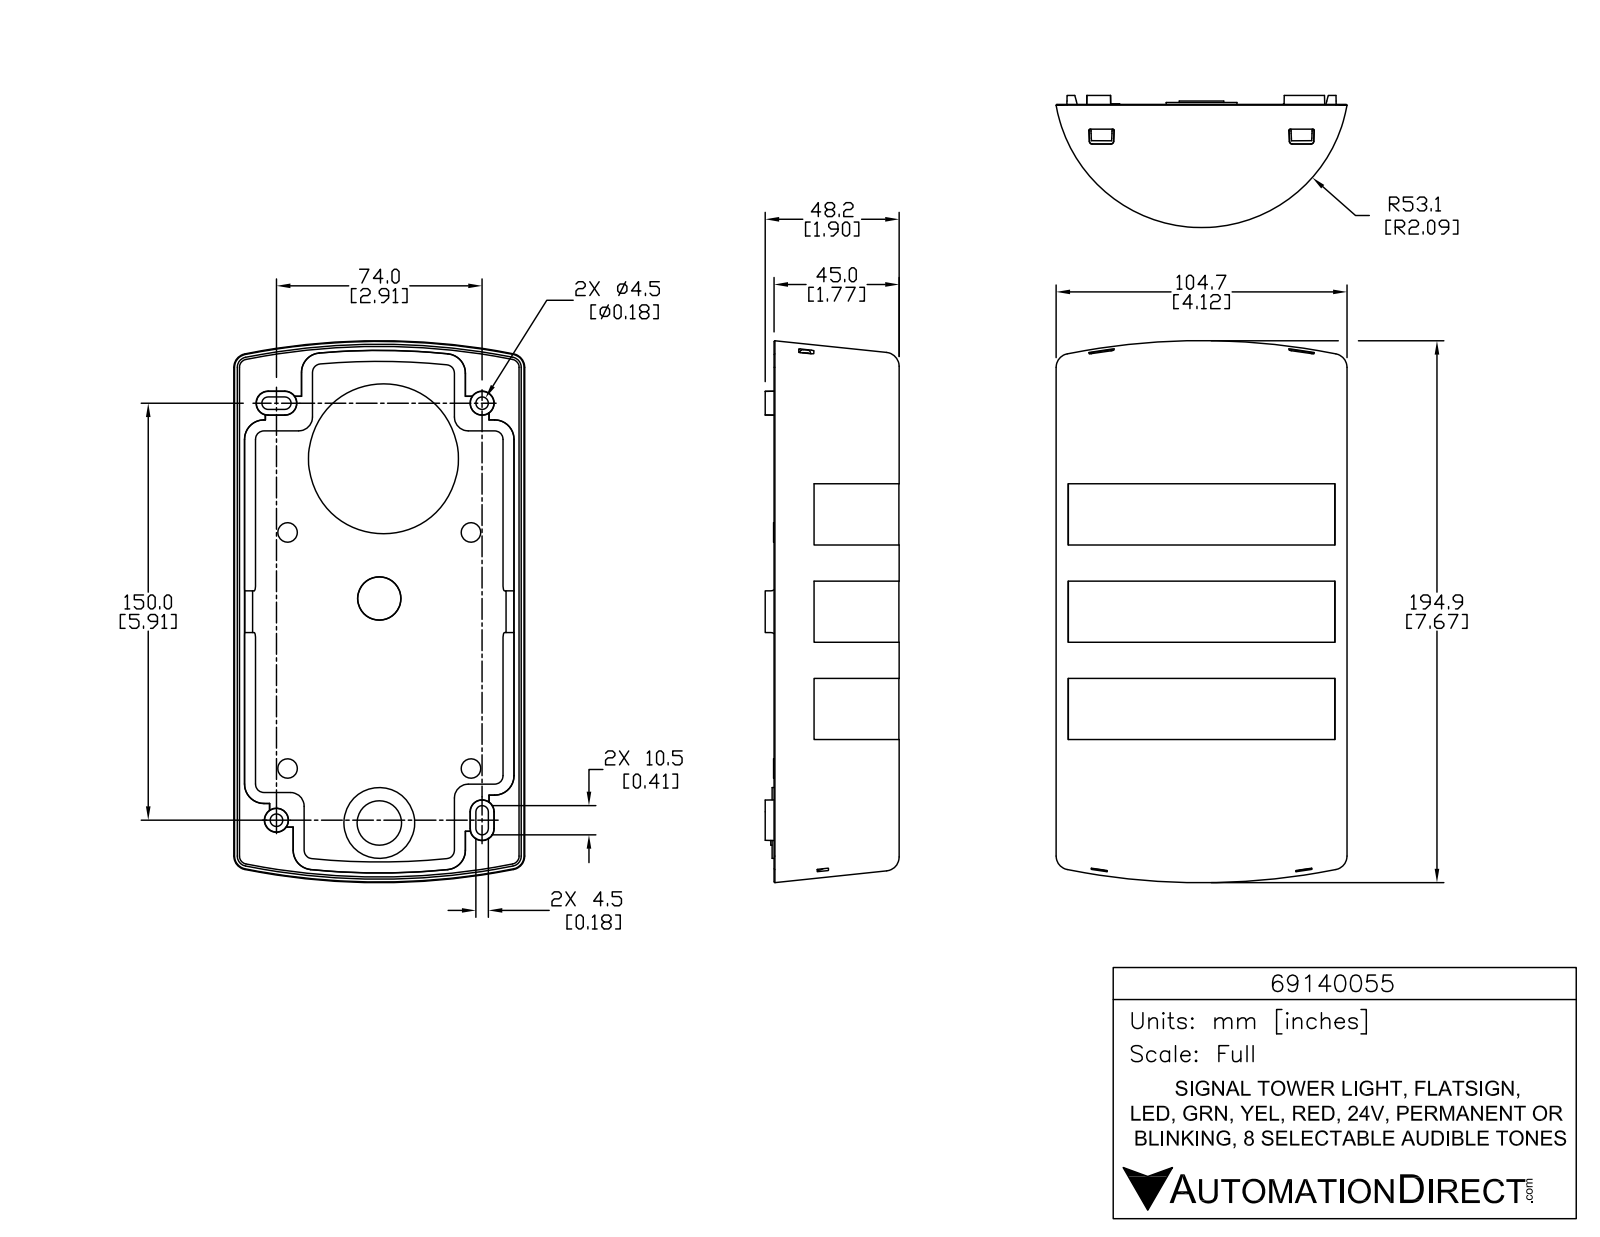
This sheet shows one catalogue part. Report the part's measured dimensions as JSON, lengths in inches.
{"part_name": "69140055", "step_written_by": "SolidWorks 2017 (AUTOMOTIVE_DESIGN)", "units": "inches", "bodies": {"solids": 1, "faces": 1074, "planar": 520, "cylindrical": 128, "other": 426}, "overall_size": [7.675, 4.122, 1.901], "volume_in3": 38.36, "surface_area_in2": 92.68, "round_holes": [[0.089, 1]], "round_bosses_or_shafts": [[2.126, 1], [1.004, 1], [0.63, 1], [0.514, 1], [0.128, 1]], "partial_cylinders_radius": [[0.039, 12], [0.012, 4], [0.008, 3], [0.008, 2], [0.018, 2], [0.019, 2], [0.019, 2], [0.02, 2]], "face_to_face_distances": [0.031, 0.079, 0.047, 0.11, 0.063, 0.157, 0.039, 0.02, 0.138, 0.118]}
